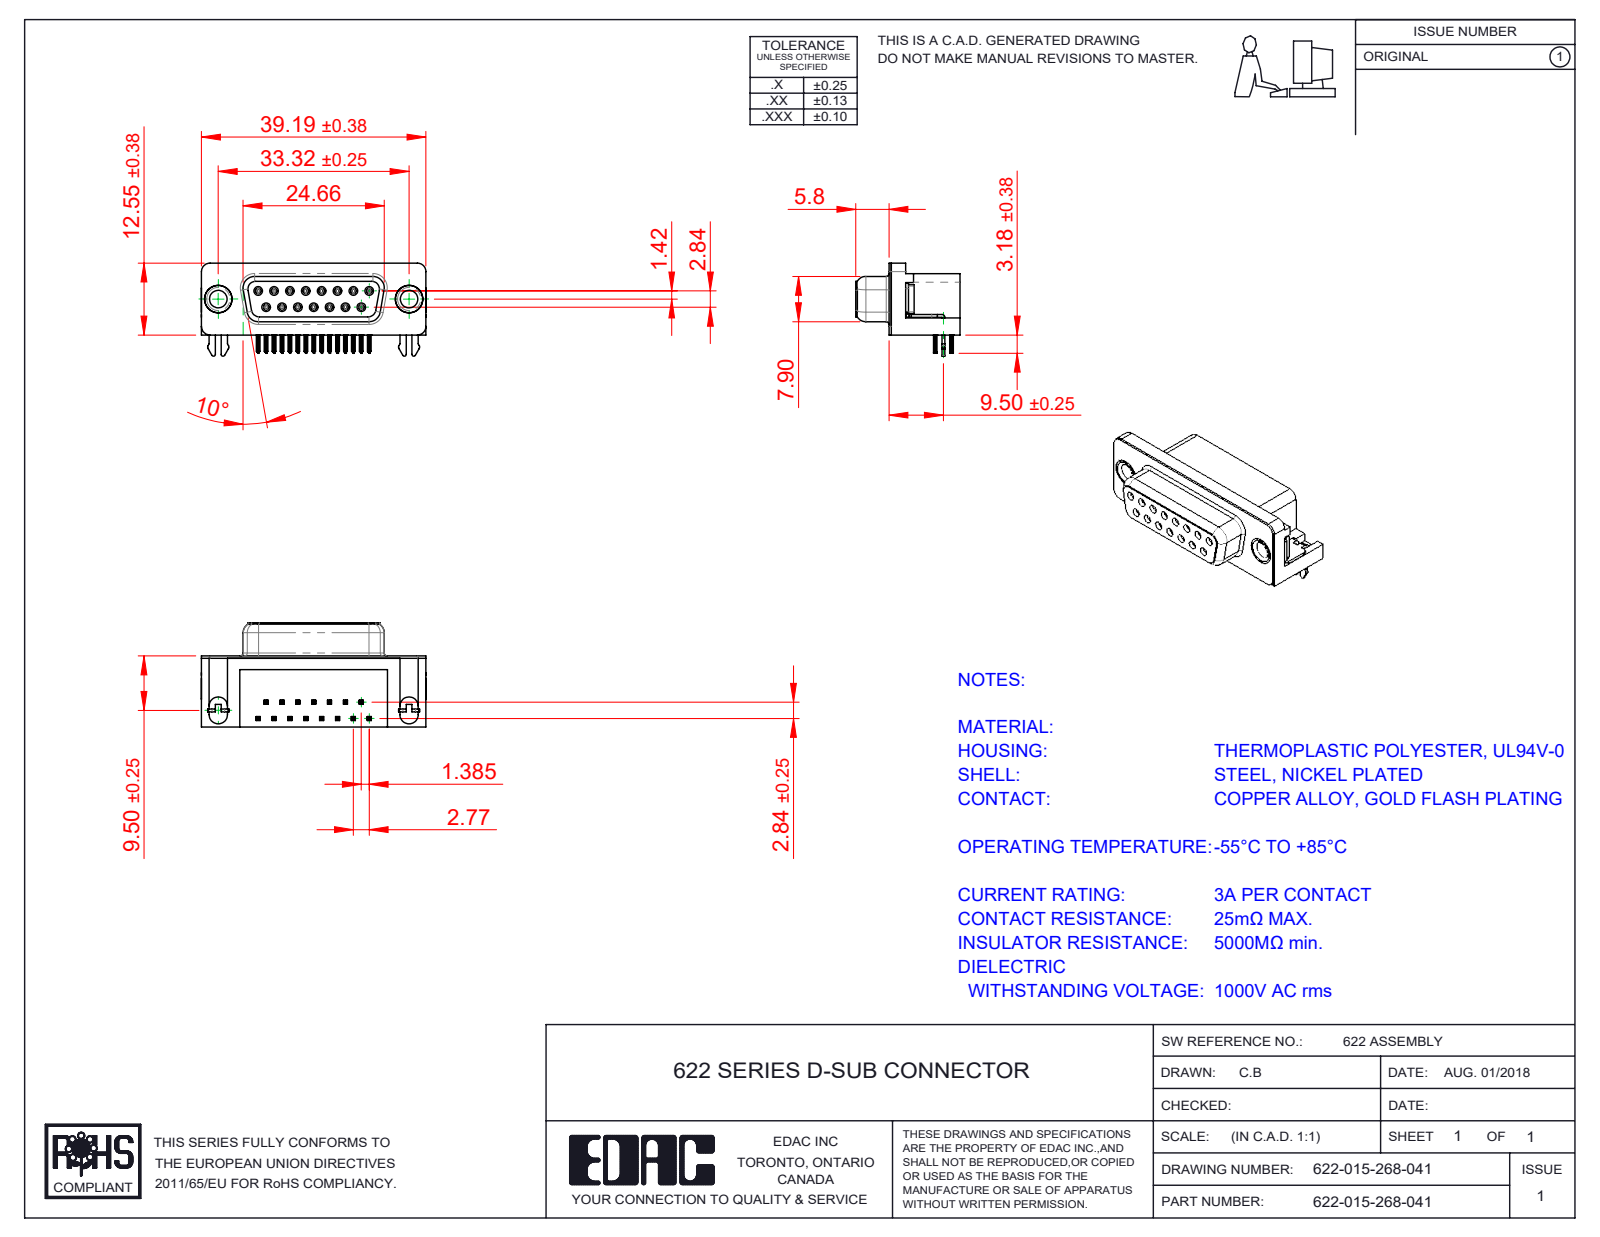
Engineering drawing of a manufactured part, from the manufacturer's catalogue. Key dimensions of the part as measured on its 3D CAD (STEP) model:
Part name (STEP PRODUCT): 622 Socket Bottom; 622 Thru Hole Rivet; 622 4 Prong Board Lock; 622 Housing_15 Socket (+3 more)
STEP written by: SolidWorks 2016 (CONFIG_CONTROL_DESIGN)
Units: millimetres
Bodies: 21 solids, 2507 faces (1116 planar, 593 cylindrical, 798 other)
Overall size (bounding box): 39.22 × 18.2 × 16.25
Volume: 5 185 mm³ · Surface area: 6 767 mm²
Round holes (diameter × count): ⌀0.8 ×15, ⌀0.9 ×15, ⌀2 ×2, ⌀3.05 ×2, ⌀4 ×2, ⌀4.8 ×2, ⌀5 ×2
Round bosses / shafts (diameter × count): ⌀1.2 ×15, ⌀4.9 ×2, ⌀4.75 ×2, ⌀3.85 ×2, ⌀3 ×2
Partial cylindrical surfaces — rounded edges, fillets, slot ends (radius × count): R0.1 ×120, R0.15 ×60, R0.35 ×30, R1 ×18, R0.34 ×15, R0.25 ×12, R1.35 ×8, R1.5 ×8
Main face-to-face distances: 0.4, 12, 6.2, 12.4, 10.35, 2.9, 6.65, 0.85, 0.35, 5.8
Hole centre spacings: 3.16, 2.77, 5.54, 8.31, 11.08, 5.03, 5.04, 7.48
